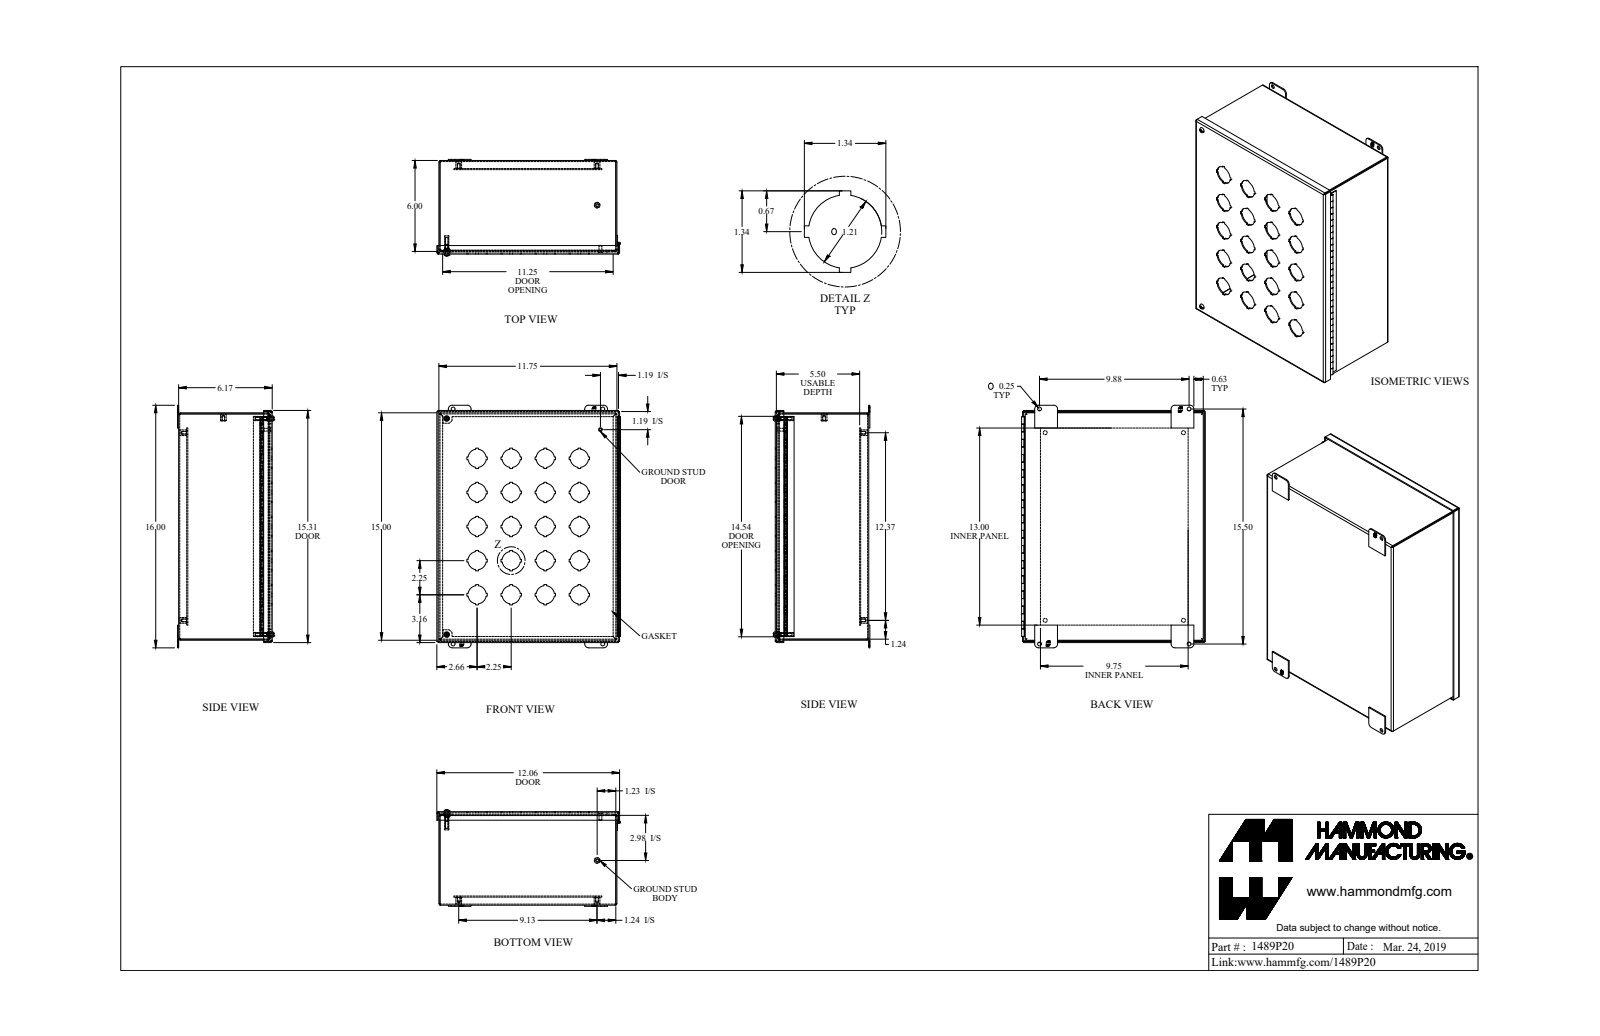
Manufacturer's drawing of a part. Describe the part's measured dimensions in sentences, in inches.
The part is named "1489P20_Default". Its 3-D file was written by "SolidWorks 2019 (CONFIG_CONTROL_DESIGN)". It is 21 solids with 1087 faces: 754 planar, 275 cylindrical and 58 other. Overall it measures 16 by 12.123 by 6.371 inches. Its volume is 67.22 cubic inches and its surface area 1 805 square inches. Round holes: 20 of diameter 1.21, 6 of diameter 0.25, 5 of diameter 0.156, 4 of diameter 0.265, 2 of diameter 0.159, 2 of diameter 0.406. Round bosses or shafts: 5 of diameter 0.375, 2 of diameter 0.39, 2 of diameter 0.275, 2 of diameter 0.19, 2 of diameter 0.148, 1 of diameter 0.25, 1 of diameter 0.188, 1 of diameter 0.174. Partial cylindrical surfaces (rounded edges, fillets, slot ends): 12 of radius 0.036, 12 of radius 0.108, 8 of radius 0.25, 2 of radius 0.16, 2 of radius 0.171, 1 of radius 0.125. The main face-to-face distances are 0.072, 6.1, 5.568, 0.532, 11.678, 0.072, 6.028, 6.172, 0.604, 14.928. The hole center spacings are 5.031, 2.25, 3.182, 4.5, 7.115, 8.113, 6.75, 6.364.
